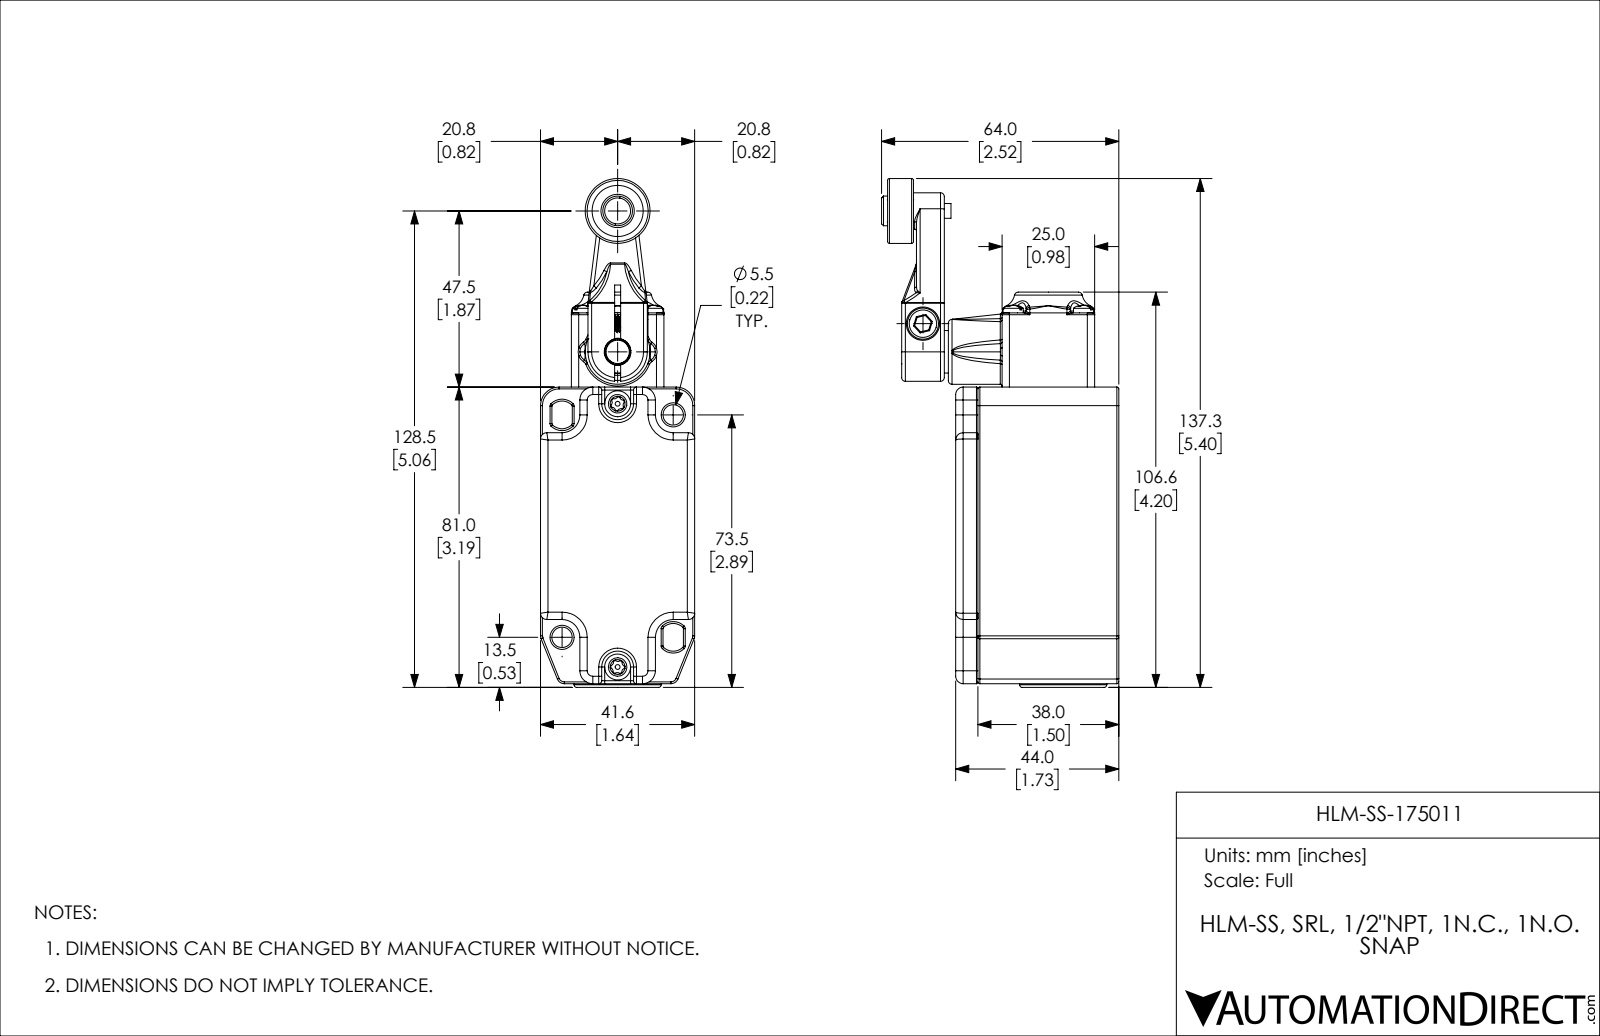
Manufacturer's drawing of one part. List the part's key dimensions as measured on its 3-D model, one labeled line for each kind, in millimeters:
Part name (STEP PRODUCT): 175-HLM-SS (short Roller lever) (step format)
STEP written by: SolidWorks 2013 (CONFIG_CONTROL_DESIGN)
Units: millimetres
Bodies: 15 solids, 2631 faces (613 planar, 542 cylindrical, 1476 other)
Overall size (bounding box): 137.25 × 64 × 41.6
Volume: 80 756 mm³ · Surface area: 53 180 mm²
Round holes (diameter × count): ⌀2.6 ×10, ⌀3.4 ×6, ⌀4.1 ×3, ⌀4 ×2, ⌀5.5 ×2, ⌀2.9 ×1, ⌀4.4 ×1, ⌀5 ×1, ⌀5.2 ×1, ⌀6.1 ×1, ⌀7.2 ×1, ⌀9 ×1
Round bosses / shafts (diameter × count): ⌀6 ×7, ⌀5.48 ×4, ⌀3 ×4, ⌀17.5 ×2, ⌀7 ×2, ⌀1.3 ×2, ⌀23.5 ×1, ⌀18.6 ×1
Partial cylindrical surfaces — rounded edges, fillets, slot ends (radius × count): R0.5 ×123, R1 ×36, R0.4 ×24, R2 ×16, R0.15 ×14, R0.8 ×10, R0.3 ×8, R3.5 ×8
Main face-to-face distances: 3.05, 38.55, 35.5, 41.6, 44, 2.5, 41.5, 6, 38, 3.8
Hole centre spacings: 19, 13.44, 31.95, 9, 10.98, 16.51, 19.04, 21.02
